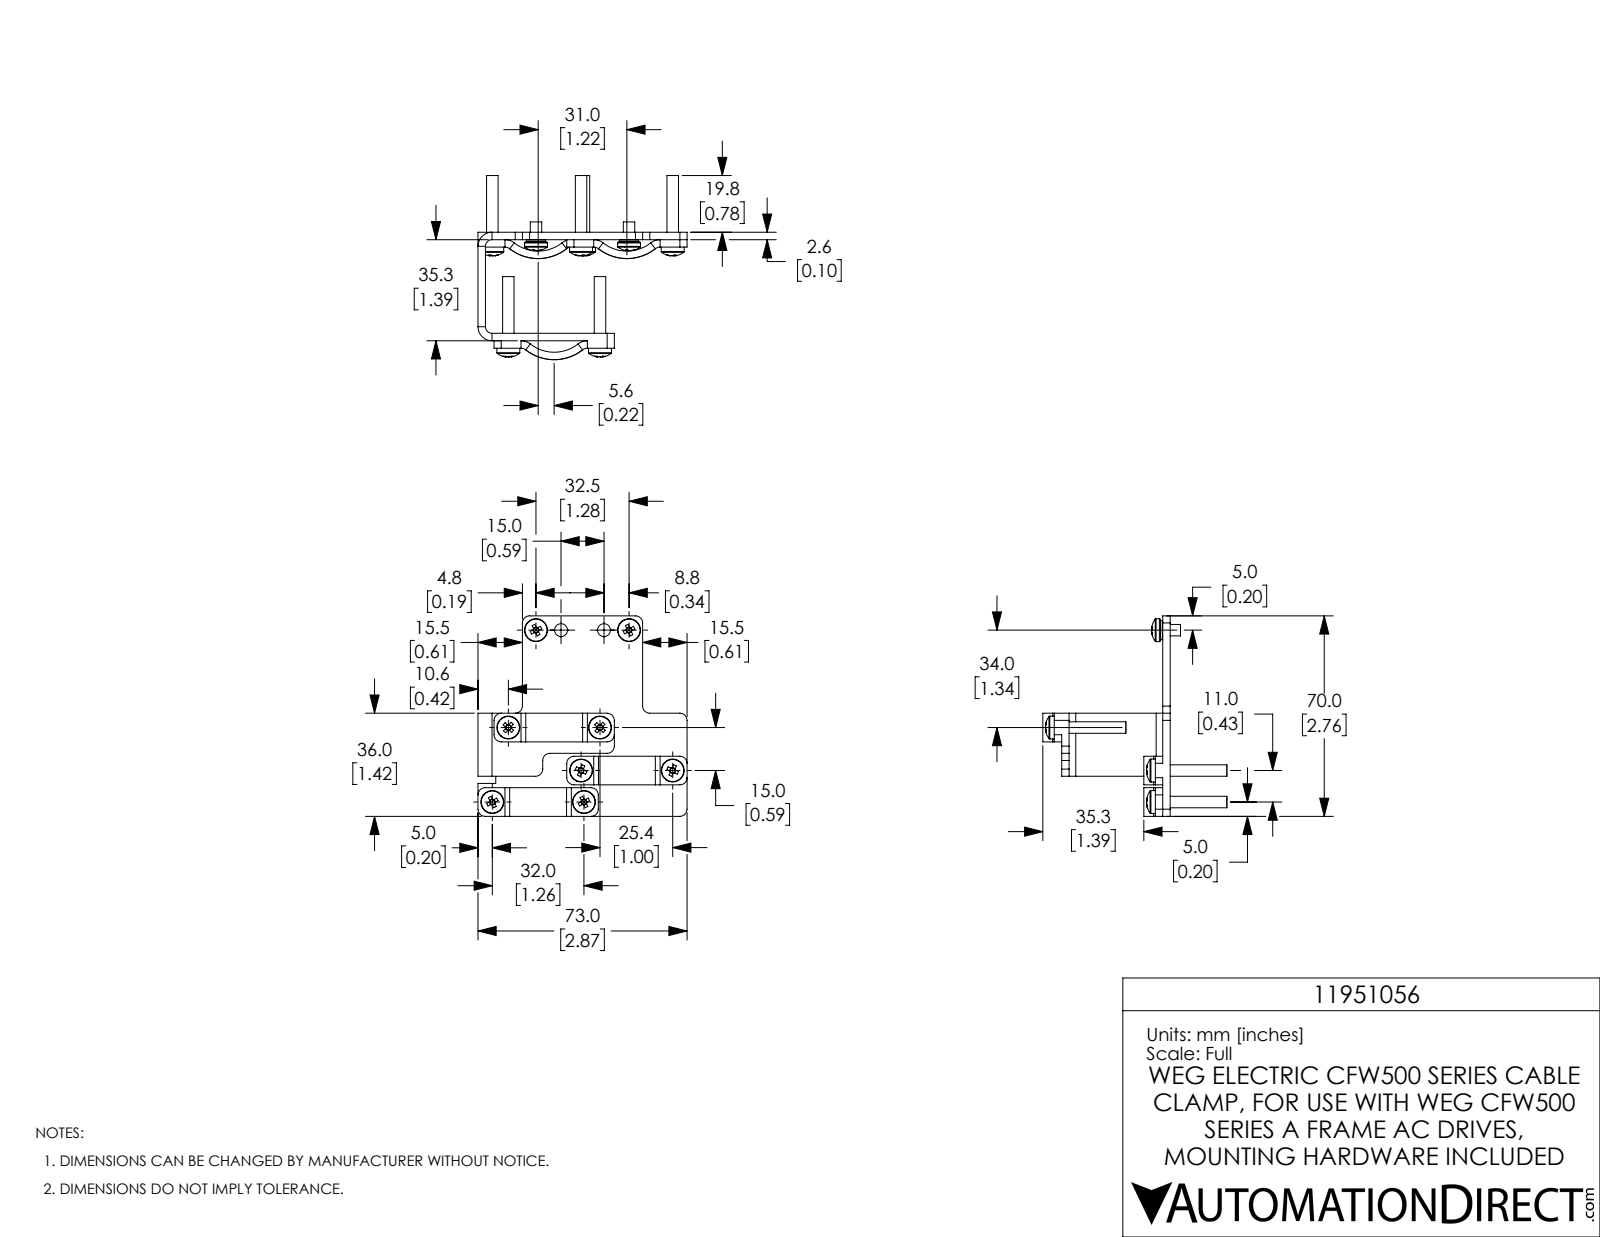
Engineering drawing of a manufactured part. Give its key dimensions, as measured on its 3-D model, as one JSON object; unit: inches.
{"part_name": "ZBC_10006124374 nc cmb1", "step_written_by": "SolidWorks 2017 (AUTOMOTIVE_DESIGN)", "units": "inches", "bodies": {"solids": 1, "faces": 462, "planar": 223, "cylindrical": 123, "other": 116}, "overall_size": [2.874, 2.756, 2.531], "volume_in3": 1.229, "surface_area_in2": 26.89, "round_holes": [[0.177, 8], [0.13, 2], [0.148, 2]], "round_bosses_or_shafts": [[0.315, 8], [0.157, 8], [0.26, 2], [0.126, 2]], "partial_cylinders_radius": [[0.098, 21], [0.106, 6], [0.209, 6], [0.531, 3], [0.634, 3], [0.091, 2], [0.193, 2]], "face_to_face_distances": [0.102, 1.39, 1.287, 1.492, 0.394, 1.417, 0.433, 0.205, 0.61, 1.024], "hole_center_spacings": [1.26, 0.344, 0.935, 1.047, 1.161, 1.295, 0.435, 0.591]}
